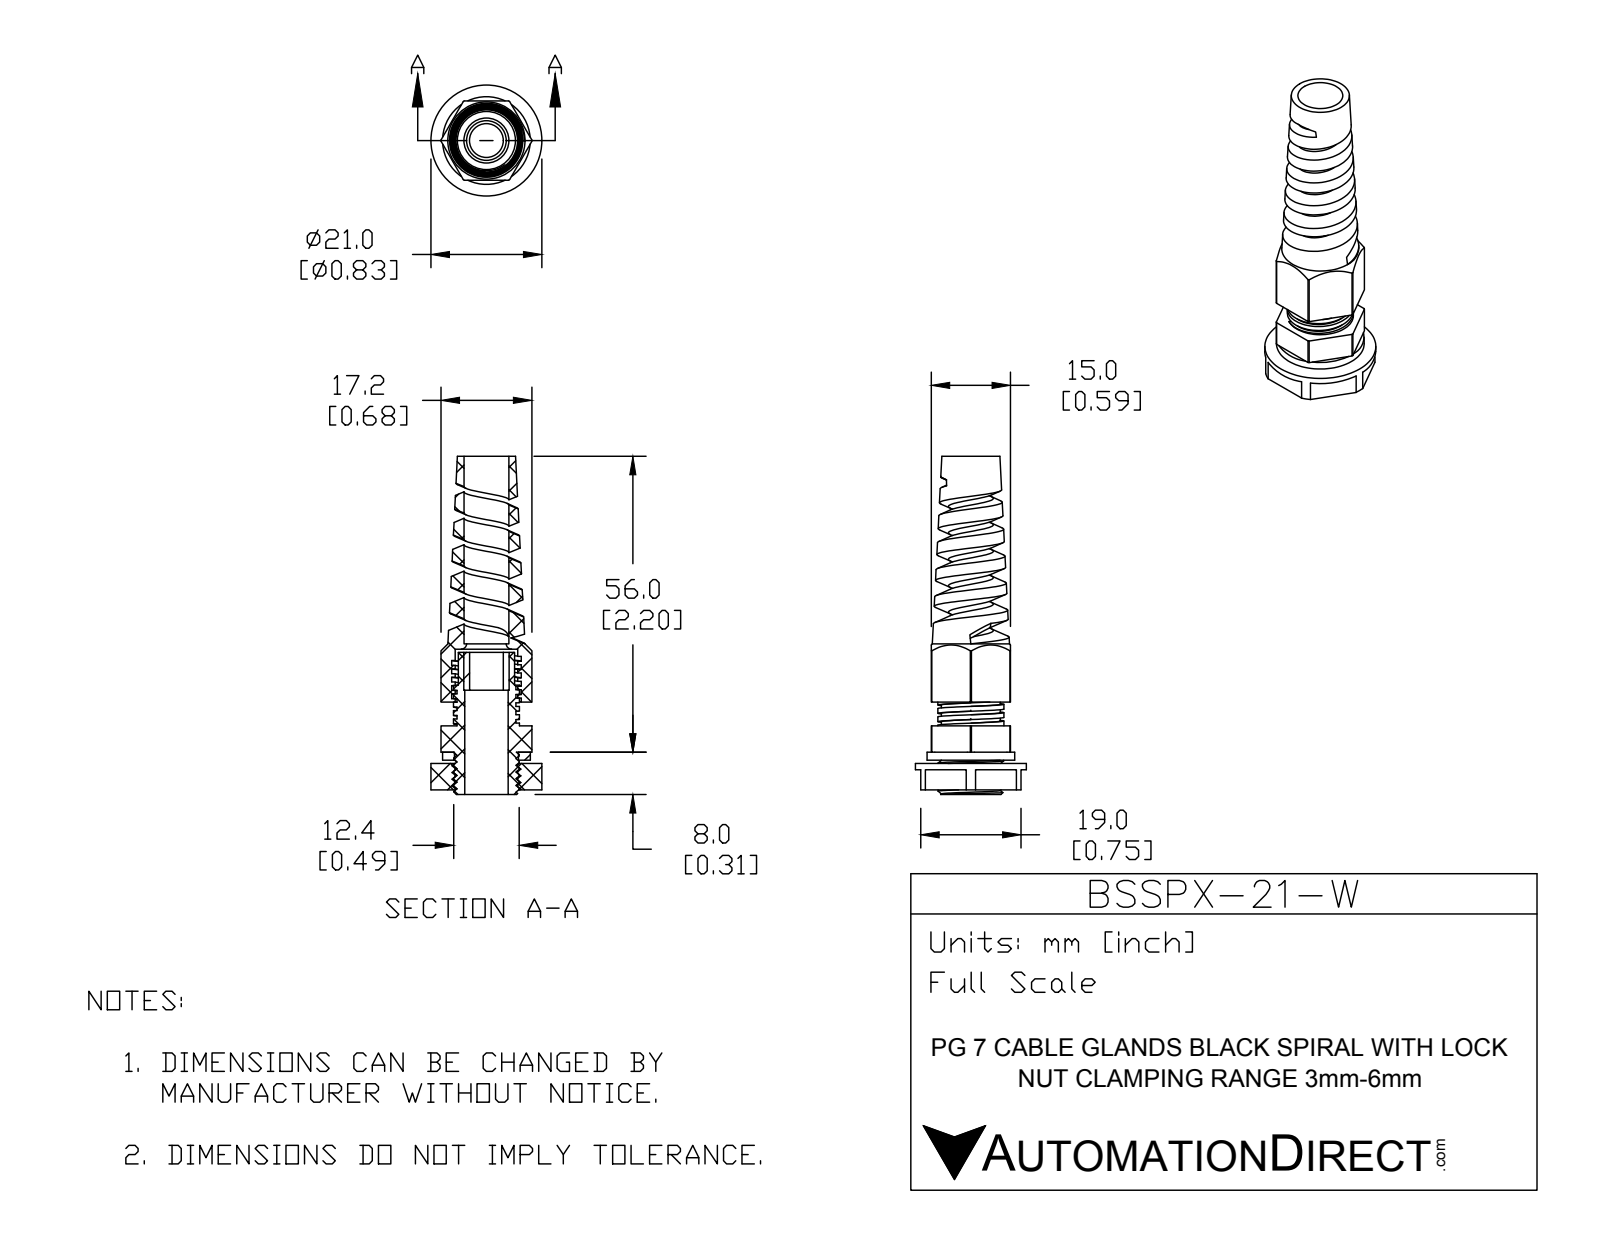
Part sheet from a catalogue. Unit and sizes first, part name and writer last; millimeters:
Units: millimetres
Overall size (bounding box): 64 × 21 × 21
Round holes (diameter × count): ⌀6.4 ×1, ⌀8.2 ×1, ⌀8.5 ×1, ⌀8.6 ×1, ⌀11.79 ×1, ⌀11.83 ×1, ⌀12.1 ×1
Round bosses / shafts (diameter × count): ⌀21 ×1, ⌀16.6 ×1, ⌀12.5 ×1, ⌀12.4 ×1, ⌀10.65 ×1
Partial cylindrical surfaces — rounded edges, fillets, slot ends (radius × count): R8.6 ×1
Main face-to-face distances: 15, 5, 17, 7.5, 2, 2.5, 6.5, 1, 19, 6
Volume: 5 677 mm³ · Surface area: 8 263 mm²
Bodies: 5 solids, 230 faces (104 planar, 90 cylindrical, 36 other)
Part name (STEP PRODUCT): BSSPX-21-W
STEP written by: SolidWorks 2015 (CONFIG_CONTROL_DESIGN)
